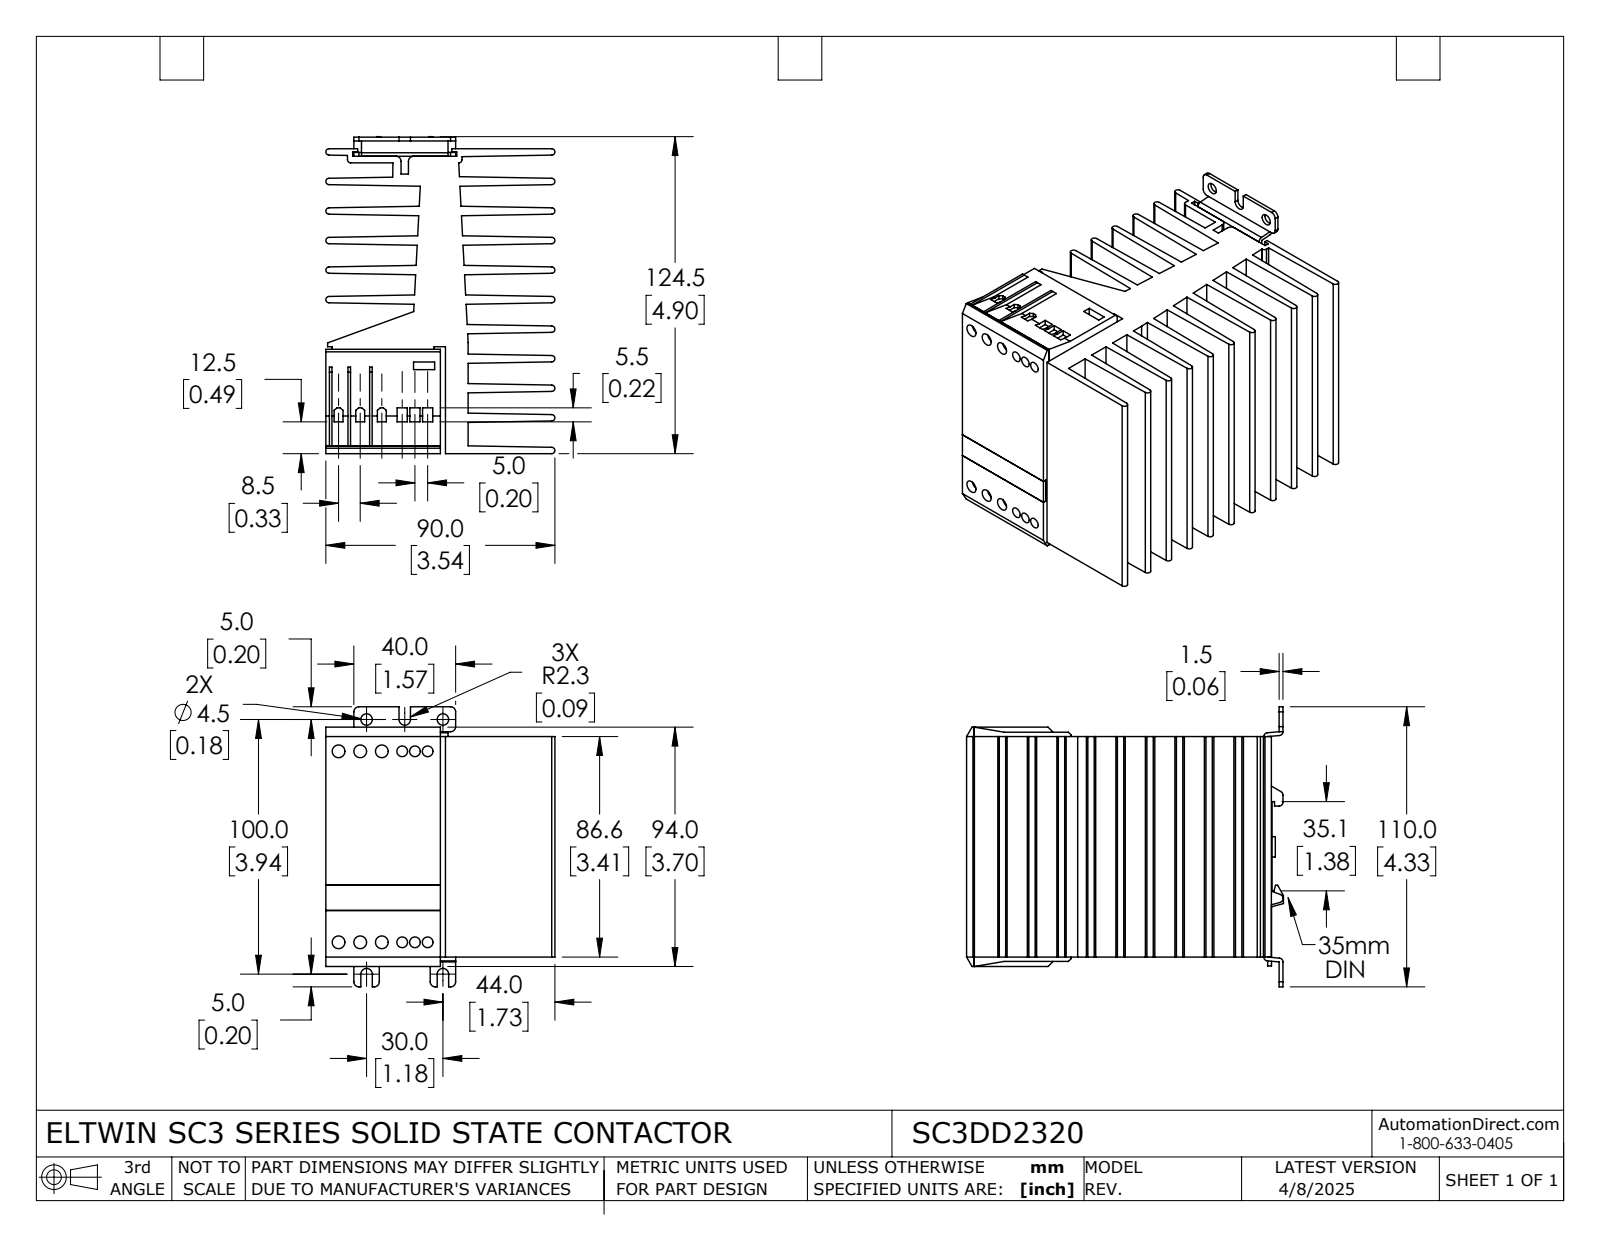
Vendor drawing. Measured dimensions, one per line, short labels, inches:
name: SC3DD2320
written by: SolidWorks 2021 (AUTOMOTIVE_DESIGN)
unit: in
bodies: 5 solids, 440 faces (326 planar, 114 cylindrical, 0 other)
size: 4.902 × 4.331 × 3.543
volume: 31.2 in³; area: 277.9 in²
holes: 6× ⌀0.165, 6× ⌀0.173, 6× ⌀0.197, 6× ⌀0.236, 2× ⌀0.177
bosses: 1× ⌀0.315
rounds: 19× R0.049, 18× R0.079, 10× R0.059, 4× R0.051, 3× R0.089
face distances: 0.457, 0.913, 1.37, 0.159, 0.3, 0.157, 1.827, 1.669, 1.828, 2.126
hole spacings: 2.953, 0.197, 0.335, 2.959, 2.972, 1.181, 0.315, 0.394
